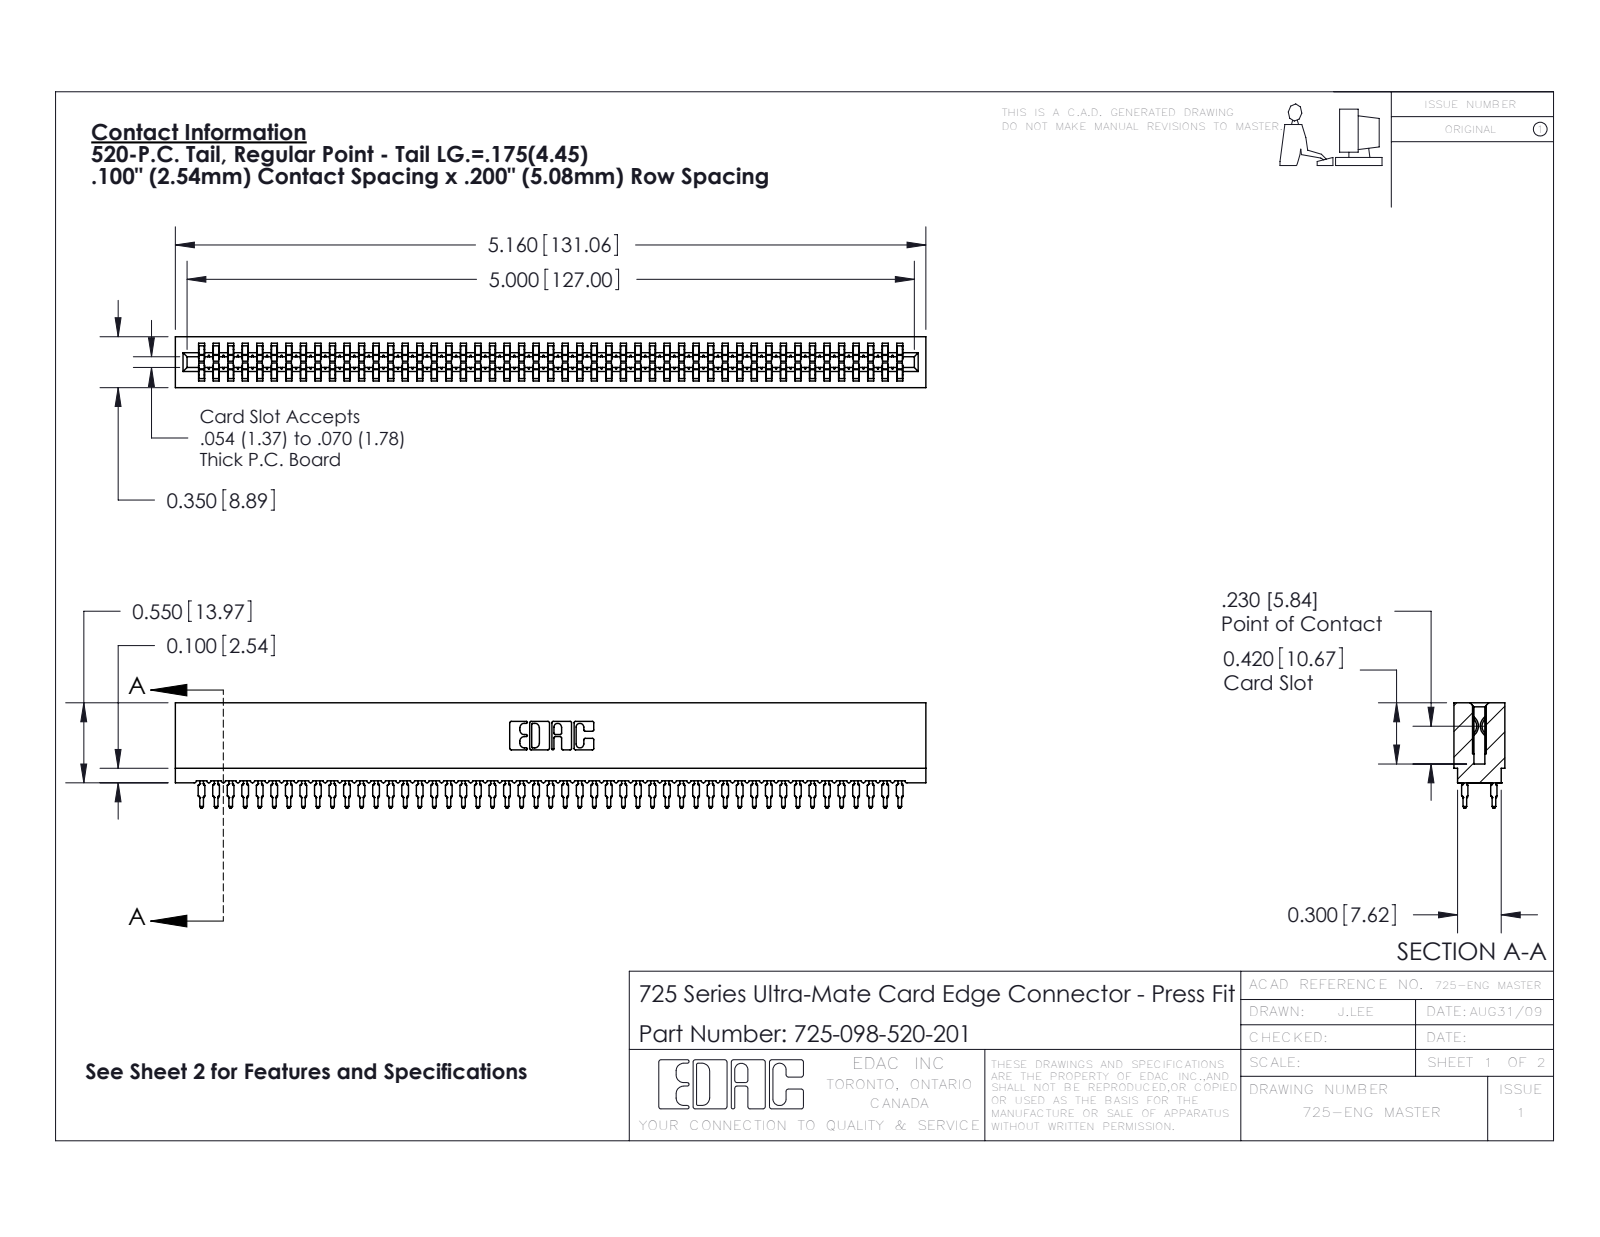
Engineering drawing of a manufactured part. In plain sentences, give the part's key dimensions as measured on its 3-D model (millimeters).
The part is named "745-292-001_520; 725-098-520-201; 725 Part_Insulator Option - 01". Its 3-D file was written by "SolidWorks 2016 (CONFIG_CONTROL_DESIGN)". It is 99 solids with 8866 faces: 4563 planar, 1755 cylindrical and 2548 other. Overall it measures 131.1 by 18.4 by 8.9 millimeters. Its volume is 10 300 cubic millimeters and its surface area 21 340 square millimeters. Partial cylindrical surfaces (rounded edges, fillets, slot ends): 196 of radius 0.5, 98 of radius 0.4, 22 of radius 0.3, 8 of radius 0.1, 8 of radius 0.3, 6 of radius 0.2, 6 of radius 0.8, 3 of radius 0.7. The main face-to-face distances are 5.1, 8.9, 1.6, 7.3, 5.4, 3.5, 1.9, 3.8, 7.7, 1.1.
